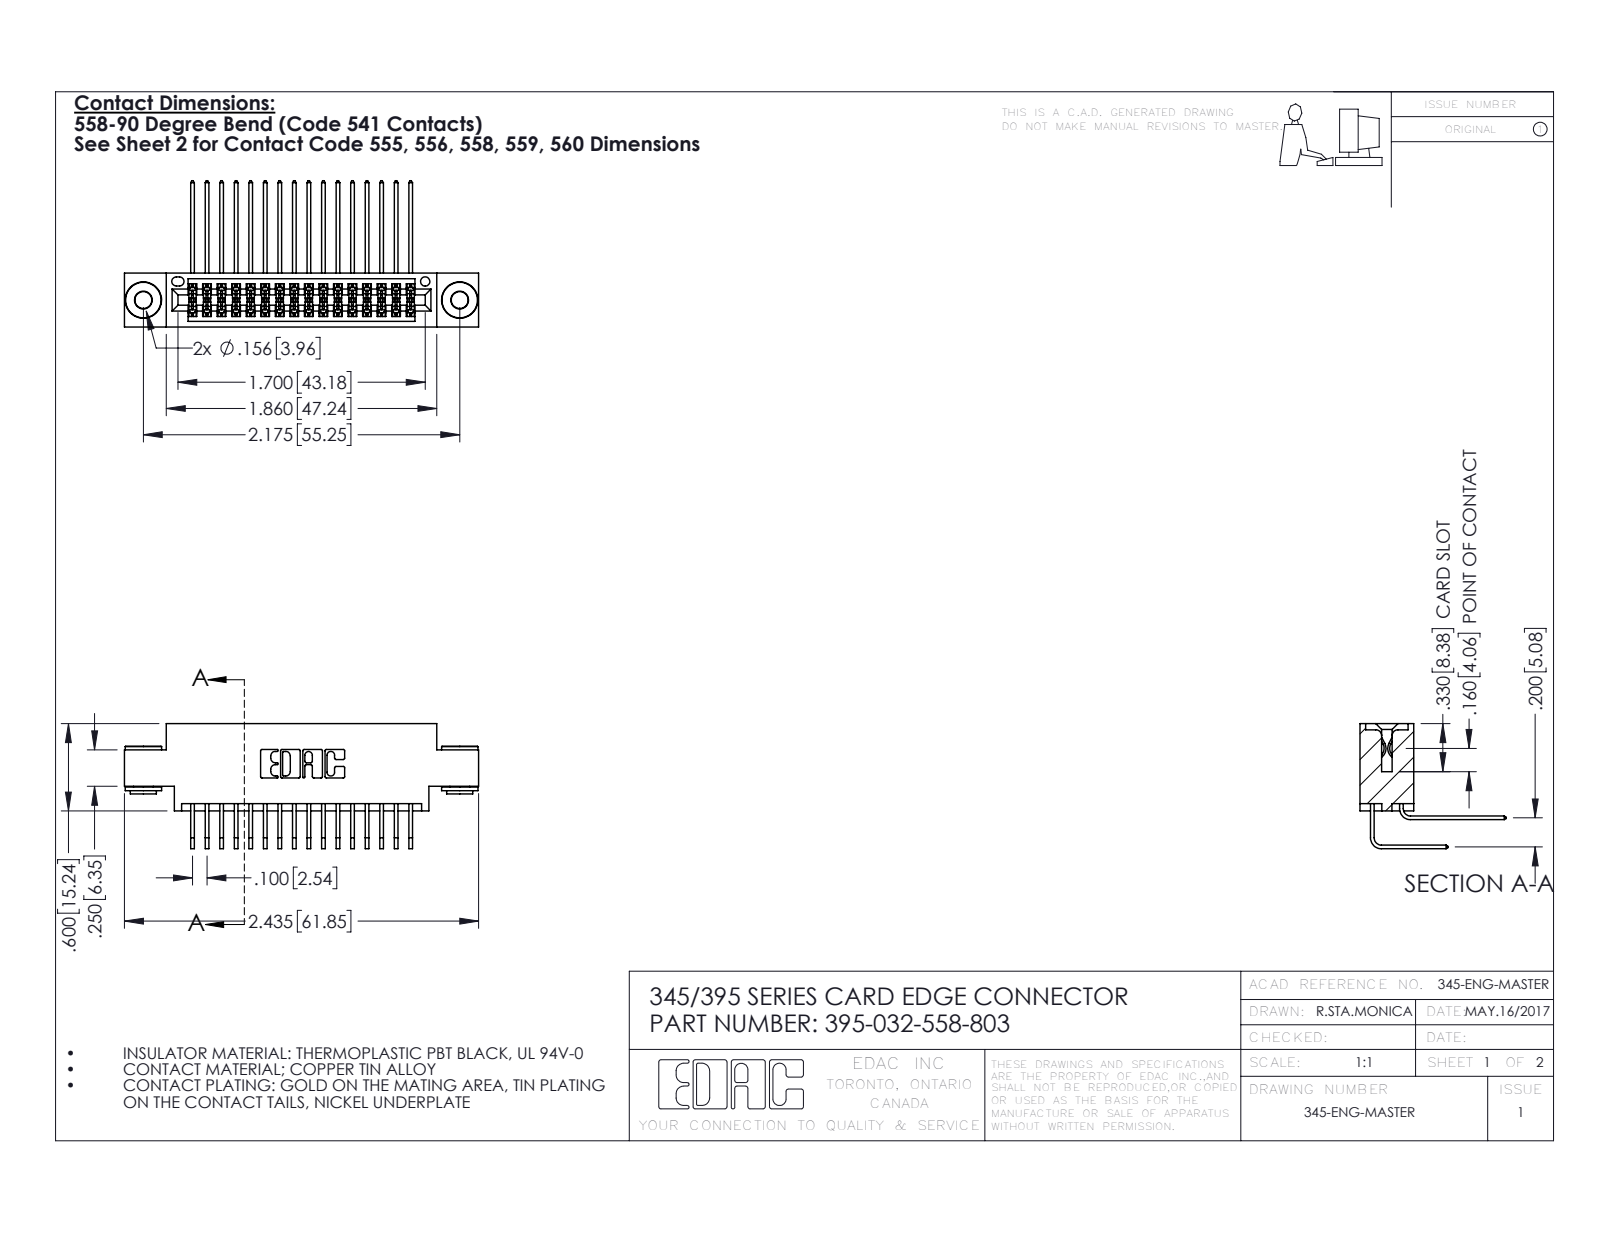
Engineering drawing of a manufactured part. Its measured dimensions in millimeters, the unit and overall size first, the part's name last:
Units: millimetres
Overall size (bounding box): 61.8 × 25.5 × 21.8
Round holes (diameter × count): ⌀2.9 ×2, ⌀4 ×2, ⌀1.6 ×1
Round bosses / shafts (diameter × count): ⌀6.4 ×2, ⌀4.6 ×2, ⌀3.5 ×2
Partial cylindrical surfaces — rounded edges, fillets, slot ends (radius × count): R0.2 ×49, R0.3 ×22, R0.2 ×6, R0.8 ×6, R0.7 ×3, R0.4 ×2, R0.5 ×2, R0.6 ×2
Main face-to-face distances: 5.1, 1.8, 7.6, 9.4, 2.5, 6.9, 0.6, 5.7, 4.4, 2.5
Hole centre spacings: 6.9, 49.3, 55.2
Volume: 5 850 mm³ · Surface area: 9 374 mm²
Bodies: 35 solids, 1832 faces (1214 planar, 610 cylindrical, 8 other)
Part name (STEP PRODUCT): 345 Part_0.170 Offset - 0.156 Dia-TH; 345-250-002_345-250-002-102; 395-032-558-803; 345-292-001_558 559 Tail - 1 (+1 more)
STEP written by: SolidWorks 2016 (CONFIG_CONTROL_DESIGN)
